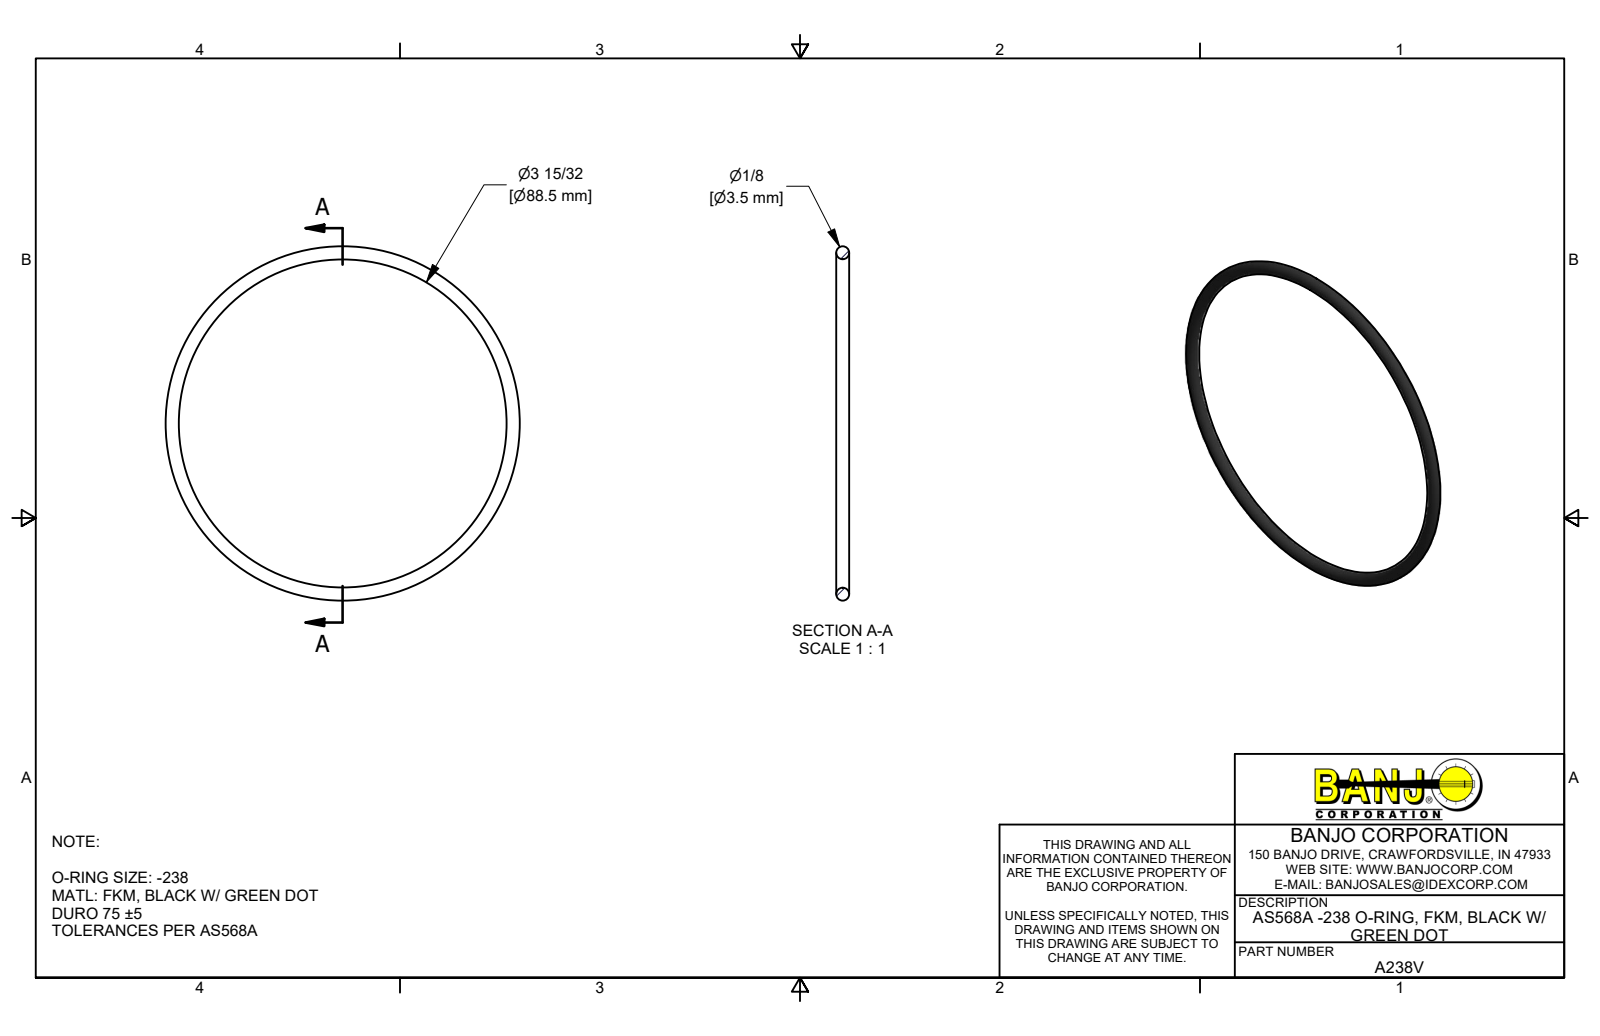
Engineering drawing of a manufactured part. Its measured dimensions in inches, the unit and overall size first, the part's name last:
Units: inches
Overall size (bounding box): 3.762 × 3.762 × 0.139
Volume: 0.173 in³ · Surface area: 4.97 in²
Bodies: 1 solid, 1 faces (0 planar, 0 cylindrical, 1 other)
Part name (STEP PRODUCT): A238V
STEP written by: Autodesk Inventor 2019 (AUTOMOTIVE_DESIGN)
